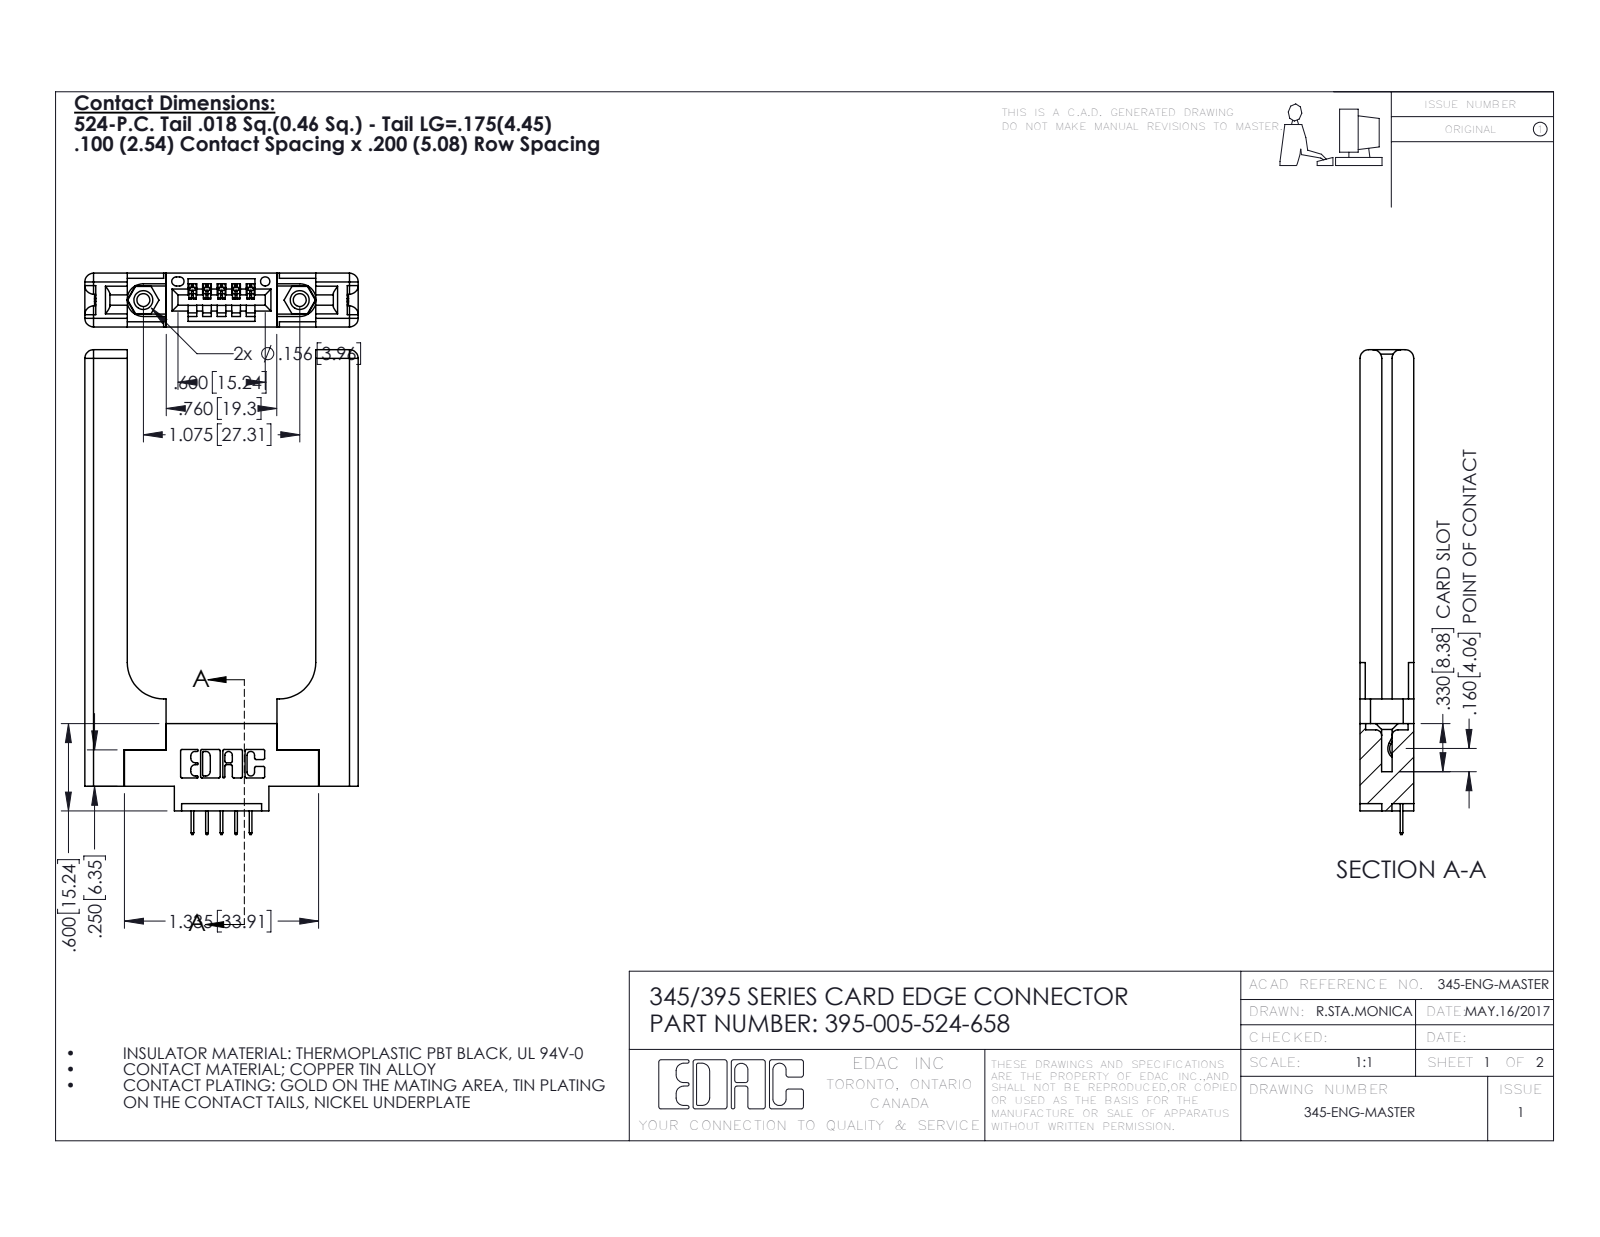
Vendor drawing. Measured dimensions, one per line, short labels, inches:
name: 395-005-524-658; 345-250-001_345-250-001-102; 345-292-001_345-293-124; 345 Part_0.170 Offset - 0.156 Dia-TH (+1 more)
written by: SolidWorks 2016 (CONFIG_CONTROL_DESIGN)
unit: in
bodies: 10 solids, 696 faces (462 planar, 174 cylindrical, 60 other)
size: 3.332 × 1.879 × 0.37
volume: 0.769 in³; area: 15.98 in²
holes: 2× ⌀0.089, 2× ⌀0.125, 2× ⌀0.156, 1× ⌀0.064
bosses: 2× ⌀0.155
rounds: 22× R0.01, 16× R0.06, 10× R0.006, 6× R0.007, 6× R0.031, 3× R0.026, 2× R0.03, 2× R0.031
face distances: 0.37, 0.15, 0.22, 1.296, 0.072, 0.071, 0.148, 0.077, 0.292, 1.587
hole spacings: 0.27, 0.847, 1.075
